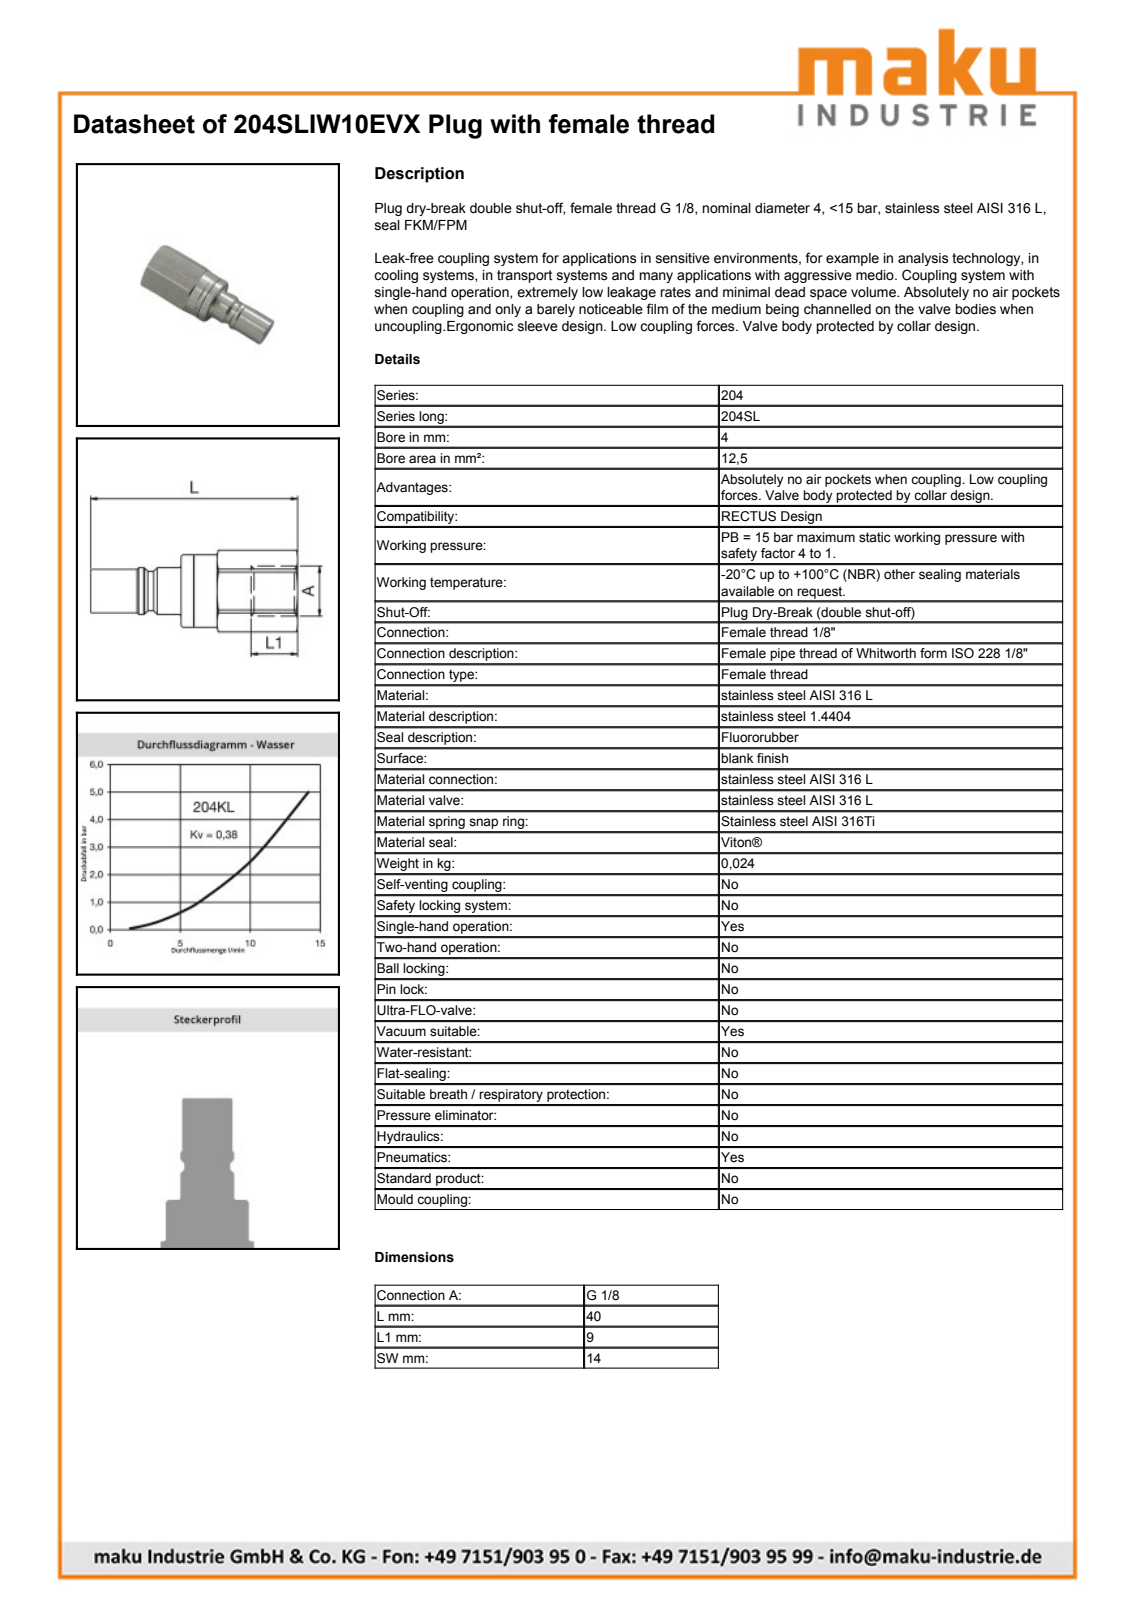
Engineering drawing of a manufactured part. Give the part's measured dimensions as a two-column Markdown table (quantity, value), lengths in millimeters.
| quantity | value |
| --- | --- |
| part name | D111060 |
| STEP written by | Autodesk Inventor 2013 (AUTOMOTIVE_DESIGN) |
| units | millimeters |
| bodies | 1 solid, 63 faces (14 planar, 21 cylindrical, 28 other) |
| overall size | 39.9 × 15.8 × 14 |
| volume | 4 101 mm³ |
| surface area | 2 680 mm² |
| round holes (diameter × count) | 6.4 × 1, 7.6 × 1, 8.57 × 1, 12 × 1 |
| round bosses / shafts (diameter × count) | 14 × 1, 11.43 × 1, 9 × 1, 8.4 × 1, 6.19 × 1 |
| partial cylindrical surfaces (radius × count) | 7.9 × 1 |
| main face-to-face distances | 14, 9, 13.4, 22.4, 17.5, 30.9, 39.9, 19.9, 2.4, 11 |
